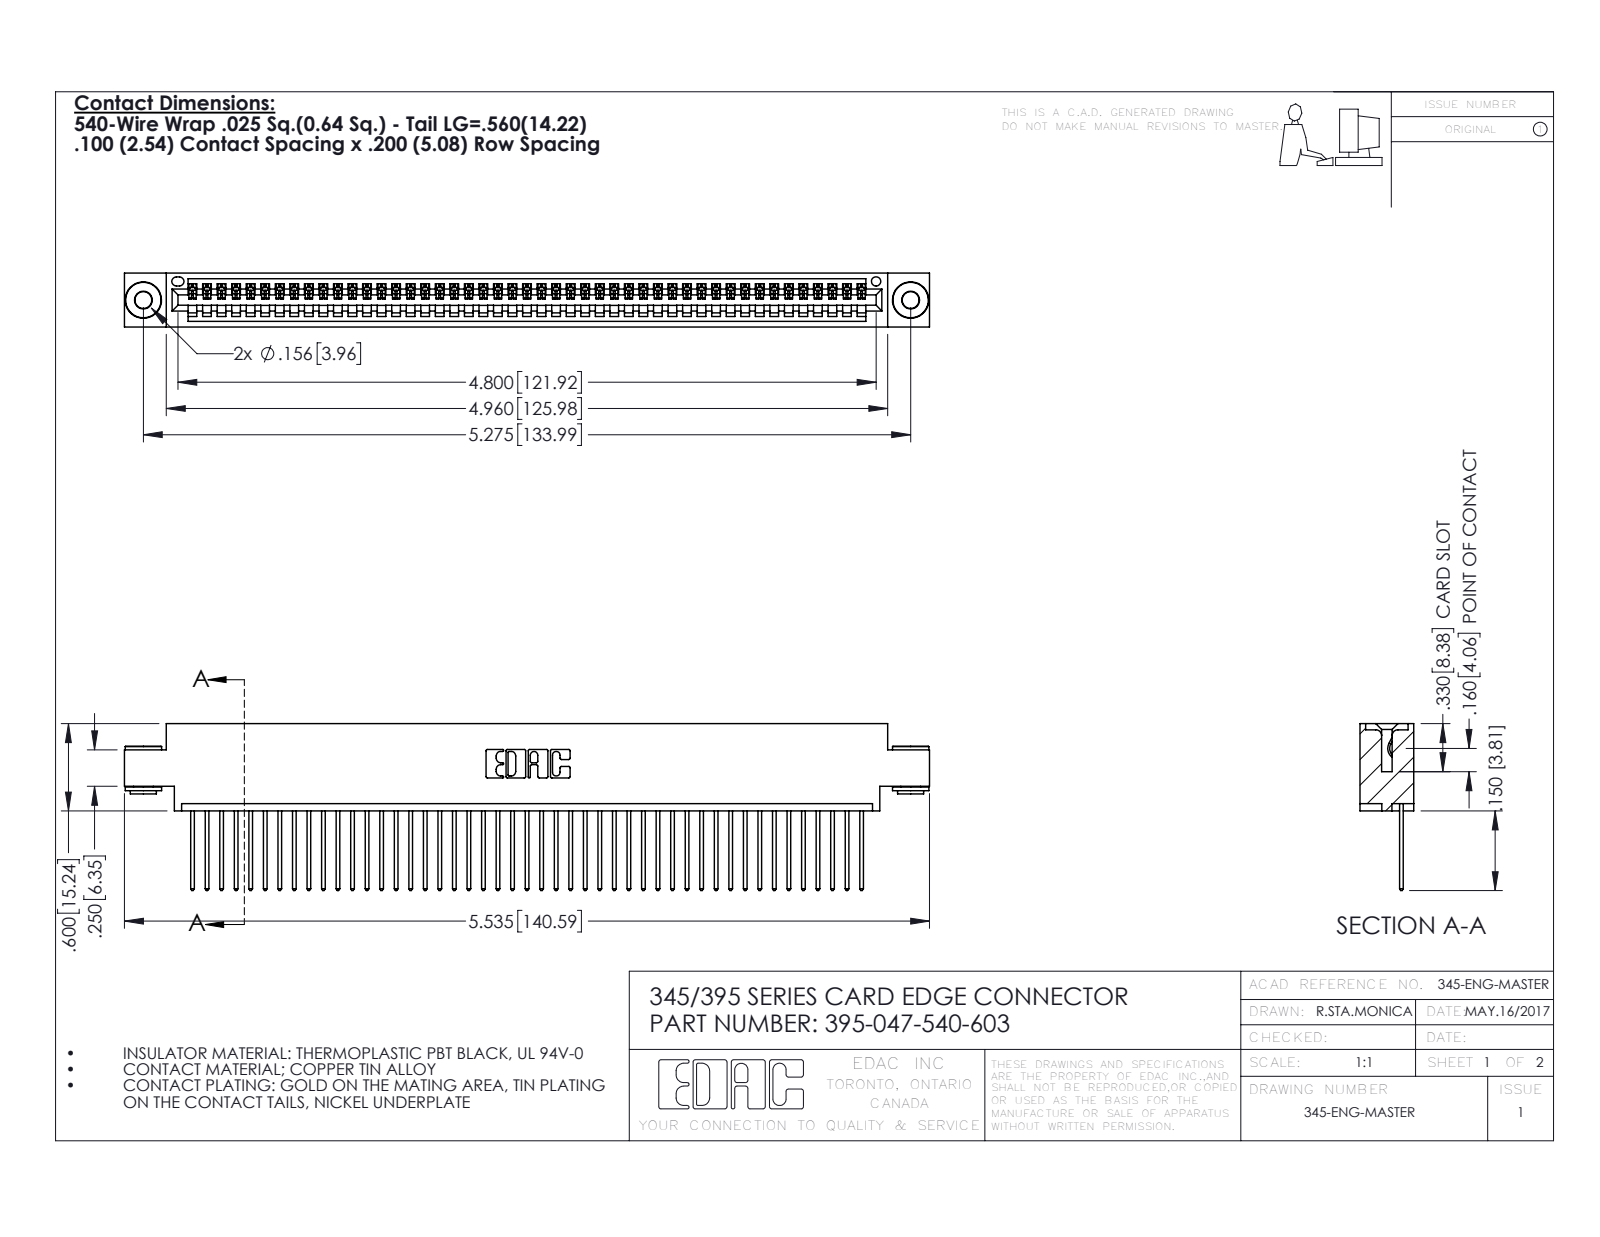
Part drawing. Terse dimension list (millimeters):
name: 345 Part_0.170 Offset - 0.156 Dia-TH; 345-250-002_345-250-002-102; 345-292-001_345-293-140; 395-047-540-603
written by: SolidWorks 2016 (CONFIG_CONTROL_DESIGN)
unit: mm
bodies: 50 solids, 2894 faces (1974 planar, 912 cylindrical, 8 other)
size: 140.6 × 29.1 × 9.4
volume: 13 400 mm³; area: 18 630 mm²
holes: 2× ⌀2.9, 2× ⌀4, 1× ⌀1.6
bosses: 2× ⌀6.4, 2× ⌀4.6, 2× ⌀3.5
rounds: 94× R0.2, 94× R0.3, 22× R0.3, 6× R0.2, 6× R0.8, 3× R0.7, 2× R0.8, 2× R1
face distances: 1.8, 7.6, 9.4, 2.5, 6.9, 0.6, 5.1, 5.7, 4.4, 3.8
hole spacings: 6.9, 128, 134
